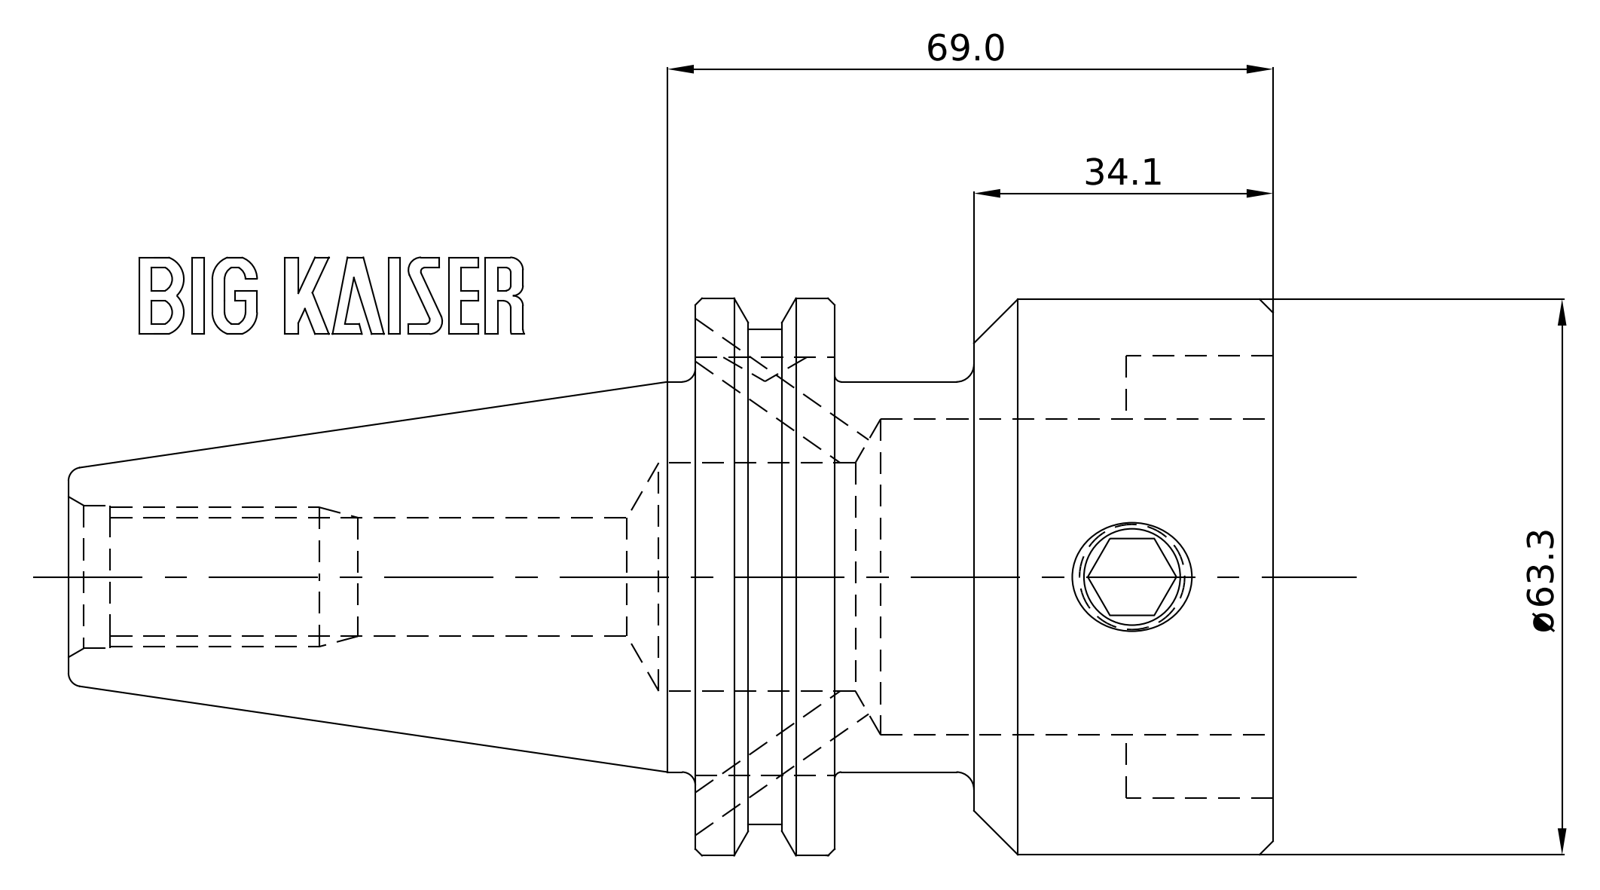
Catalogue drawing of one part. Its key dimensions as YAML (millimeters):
part_name: "11.326.862"
step_written_by: "SolidWorks 2021 (CONFIG_CONTROL_DESIGN)"
units: millimeters
bodies: {solids: 1, faces: 16, planar: 7, cylindrical: 6, other: 3}
overall_size: [137.25, 63.5, 63.5]
volume: 248883
surface_area: 29290
round_bosses_or_shafts:
  - {diameter: 63.5, count: 1}
  - {diameter: 63.27, count: 1}
  - {diameter: 56.36, count: 1}
  - {diameter: 44.45, count: 1}
face_to_face_distances: [65.83, 49.95, 15.88, 33.95, 16, 31.88, 137.25, 103.3, 87.3, 71.42]
